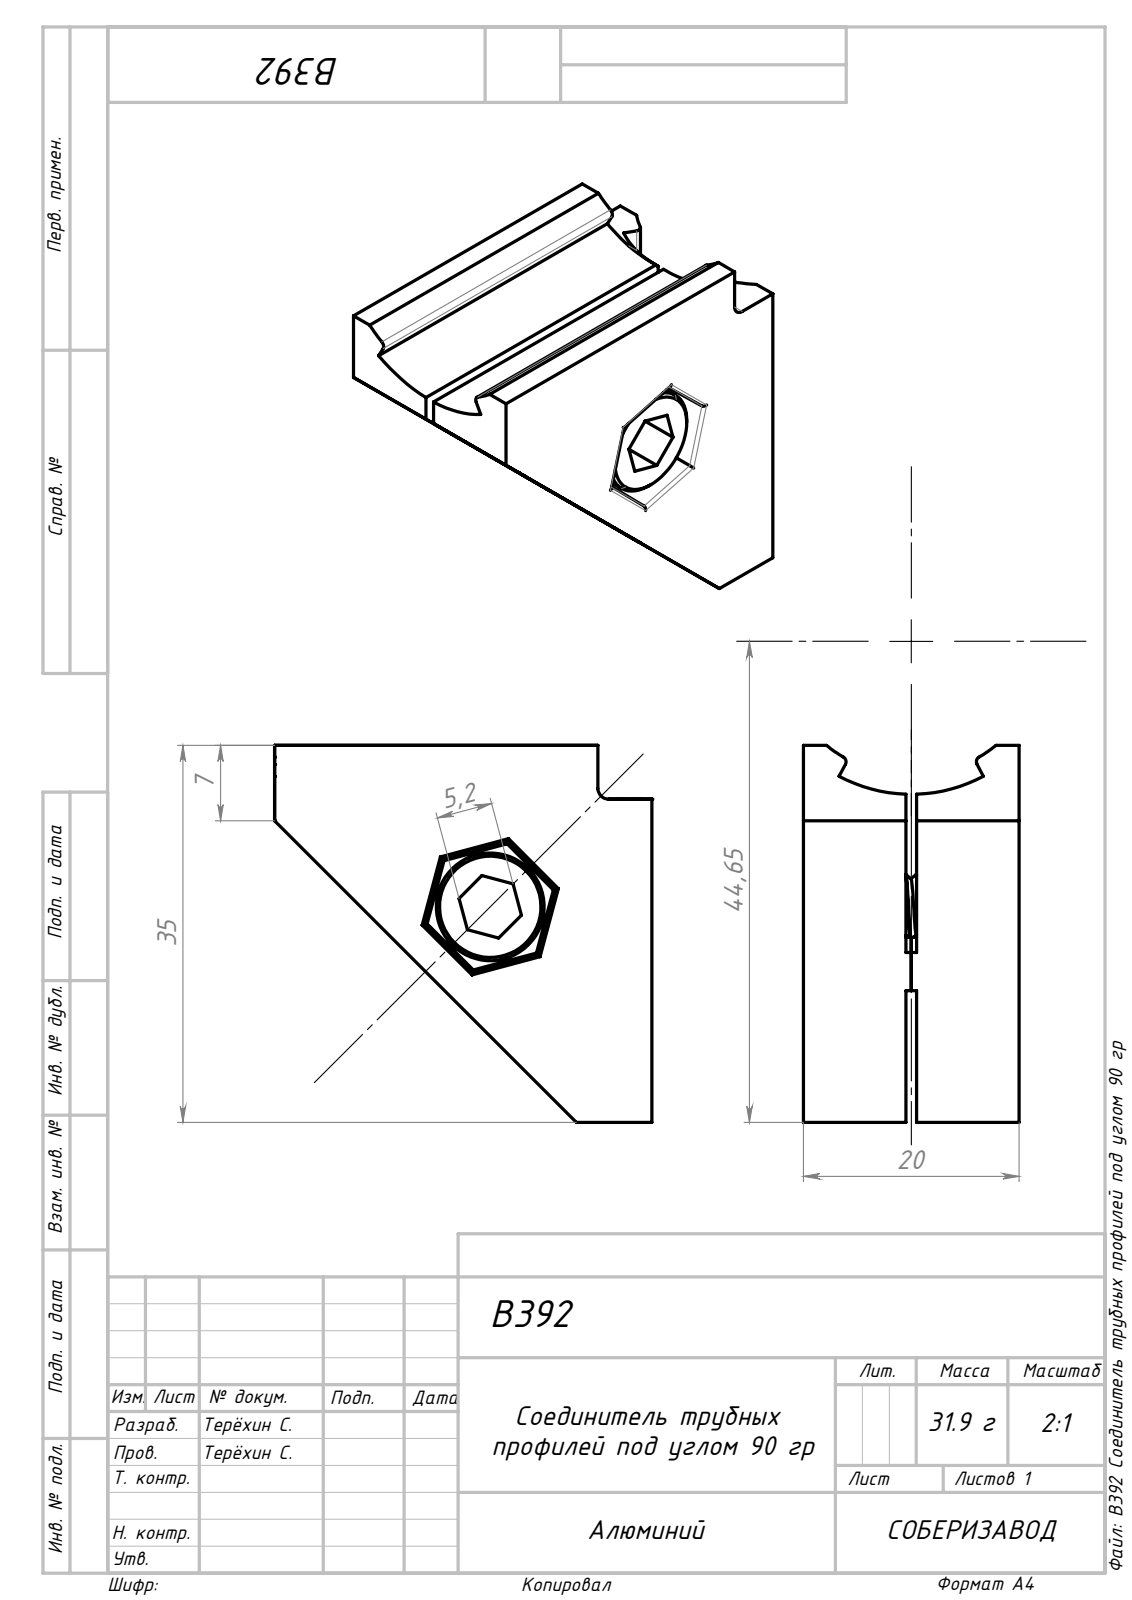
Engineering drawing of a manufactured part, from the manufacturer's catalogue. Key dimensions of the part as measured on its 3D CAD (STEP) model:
Part name (STEP PRODUCT): B392 Соединитель трубных профилей под углом 90 гр
STEP written by: SolidWorks 2022 (AUTOMOTIVE_DESIGN)
Units: millimetres
Bodies: 4 solids, 213 faces (86 planar, 80 cylindrical, 47 other)
Overall size (bounding box): 35 × 35 × 20
Volume: 10 191 mm³ · Surface area: 7 964 mm²
Round holes (diameter × count): ⌀5.2 ×1, ⌀6.5 ×1
Round bosses / shafts (diameter × count): ⌀10 ×1, ⌀6 ×1
Partial cylindrical surfaces — rounded edges, fillets, slot ends (radius × count): R0.5 ×22, R0.3 ×12, R12.45 ×2, R14.2 ×2, R1 ×1
Main face-to-face distances: 10.5, 9.5, 20, 2.5, 7, 1, 8, 3.5, 17.5, 4.5
